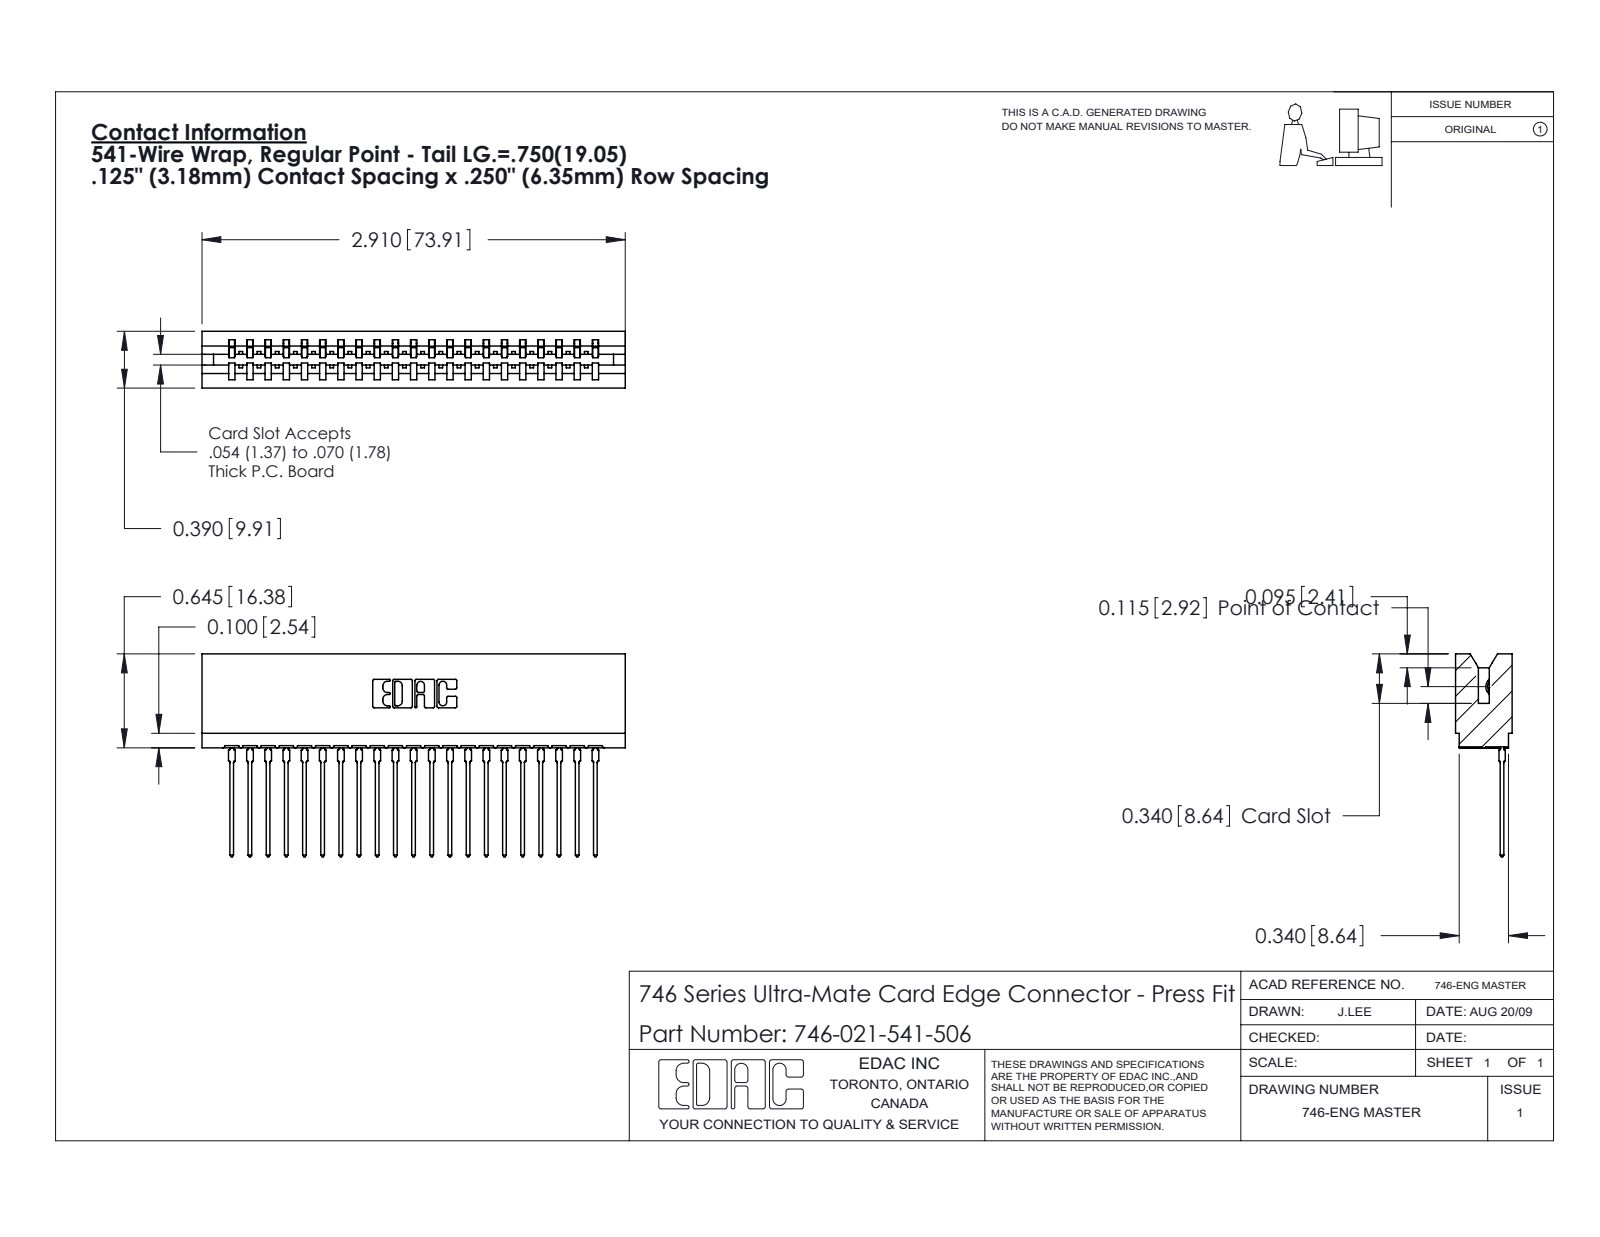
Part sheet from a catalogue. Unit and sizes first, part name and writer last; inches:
Units: inches
Overall size (bounding box): 2.91 × 1.394 × 0.39
Partial cylindrical surfaces — rounded edges, fillets, slot ends (radius × count): R0.021 ×42, R0.01 ×22, R0.015 ×22, R0.007 ×6, R0.031 ×6, R0.005 ×4, R0.011 ×4, R0.026 ×3
Main face-to-face distances: 0.333, 0.25, 0.057, 0.39, 0.5, 0.025, 0.307, 0.083, 0.042, 0.125
Volume: 0.519 in³ · Surface area: 18.1 in²
Bodies: 22 solids, 2366 faces (1379 planar, 441 cylindrical, 546 other)
Part name (STEP PRODUCT): 746-021-541-506; 746 Part_.340 Slot Depth - 06; 746-292-001_541
STEP written by: SolidWorks 2020 (CONFIG_CONTROL_DESIGN)
